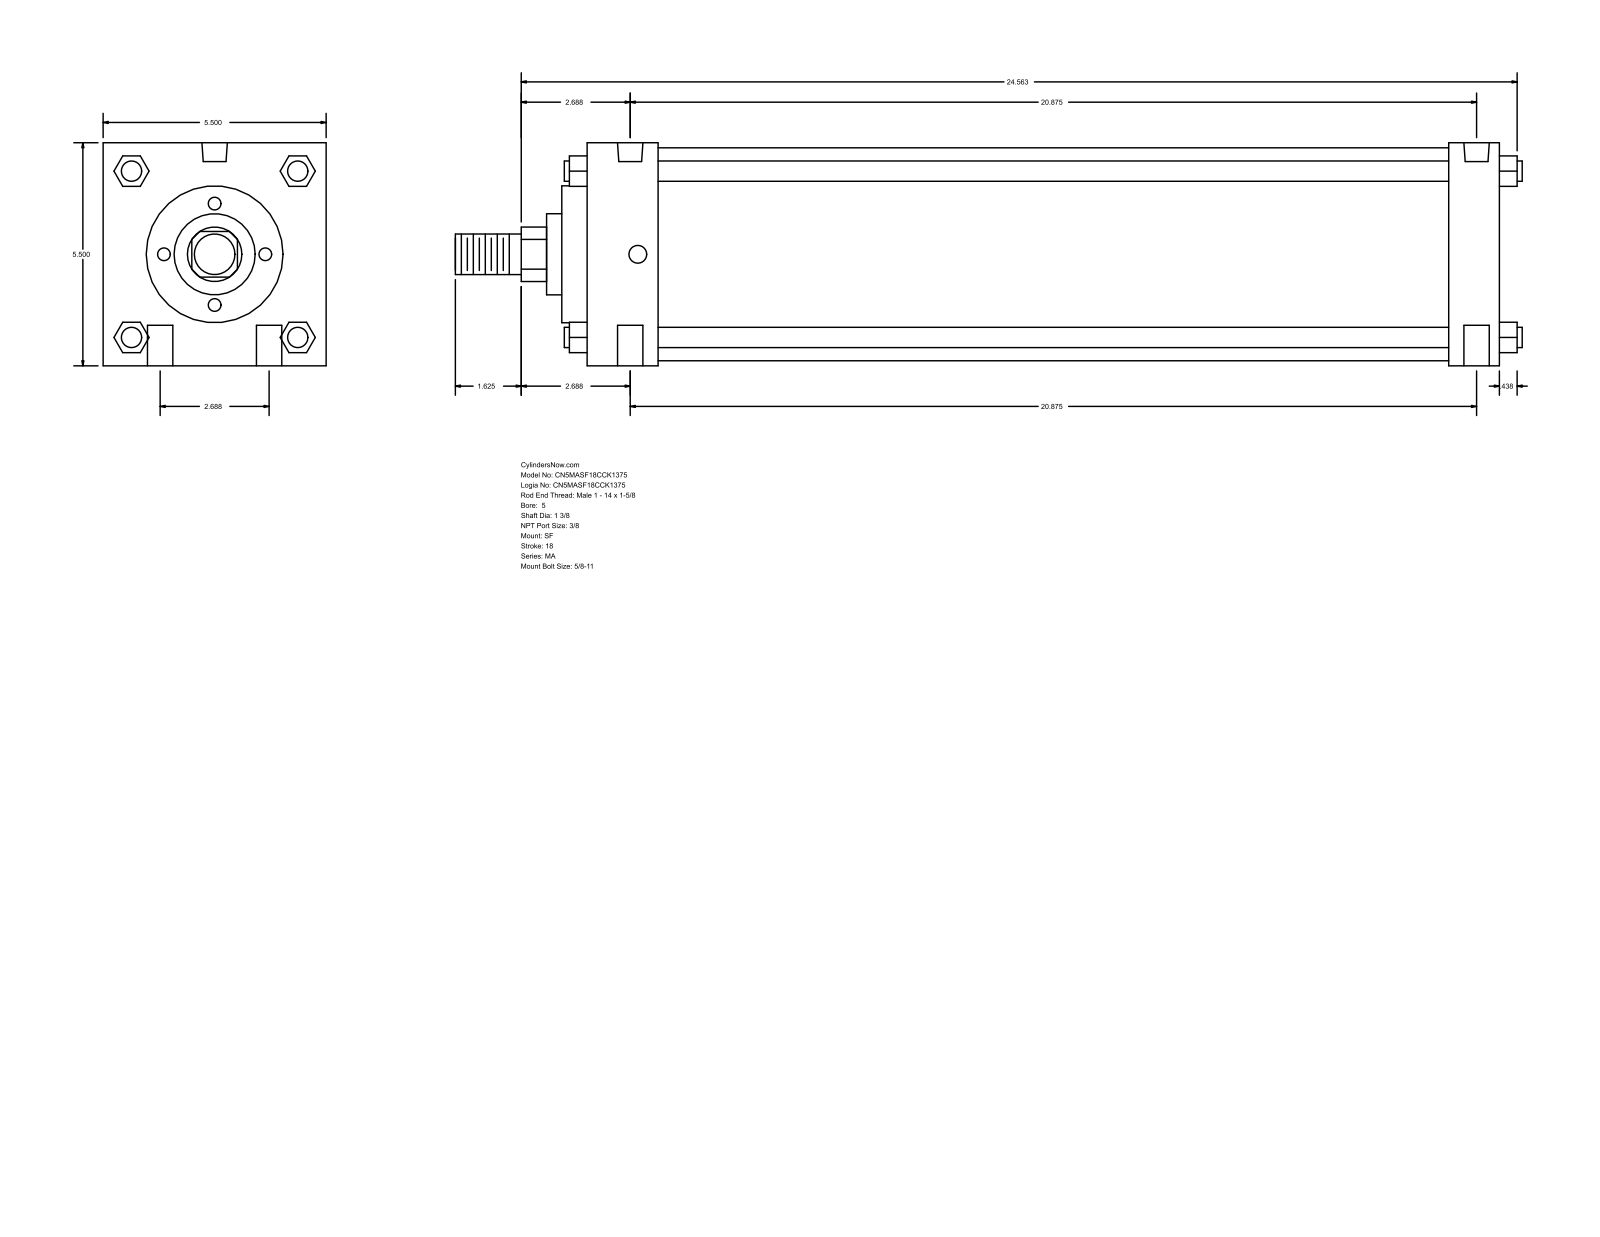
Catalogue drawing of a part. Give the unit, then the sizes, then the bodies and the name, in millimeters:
Units: millimetres
Overall size (bounding box): 668.34 × 139.7 × 139.7
Round holes (diameter × count): ⌀15.88 ×4, ⌀11.11 ×2, ⌀15.93 ×2
Round bosses / shafts (diameter × count): ⌀12.7 ×4, ⌀133.35 ×1, ⌀85.72 ×1, ⌀50.8 ×1, ⌀34.92 ×1, ⌀25.4 ×1
Partial cylindrical surfaces — rounded edges, fillets, slot ends (radius × count): R17.06 ×1
Main face-to-face distances: 139.7, 571.5, 44.45, 539.75, 495.3, 527.05, 31.75, 15.87, 60.32, 555.62
Hole centre spacings: 34.13, 531.33, 530.23, 68.26, 534.61, 520.7
Bodies: 0 solids, 126 faces (95 planar, 31 cylindrical, 0 other)
Part name (STEP PRODUCT): MA_SF__0500_1.375
STEP written by: GSSL Pune (CONFIG_CONTROL_DESIGN)
